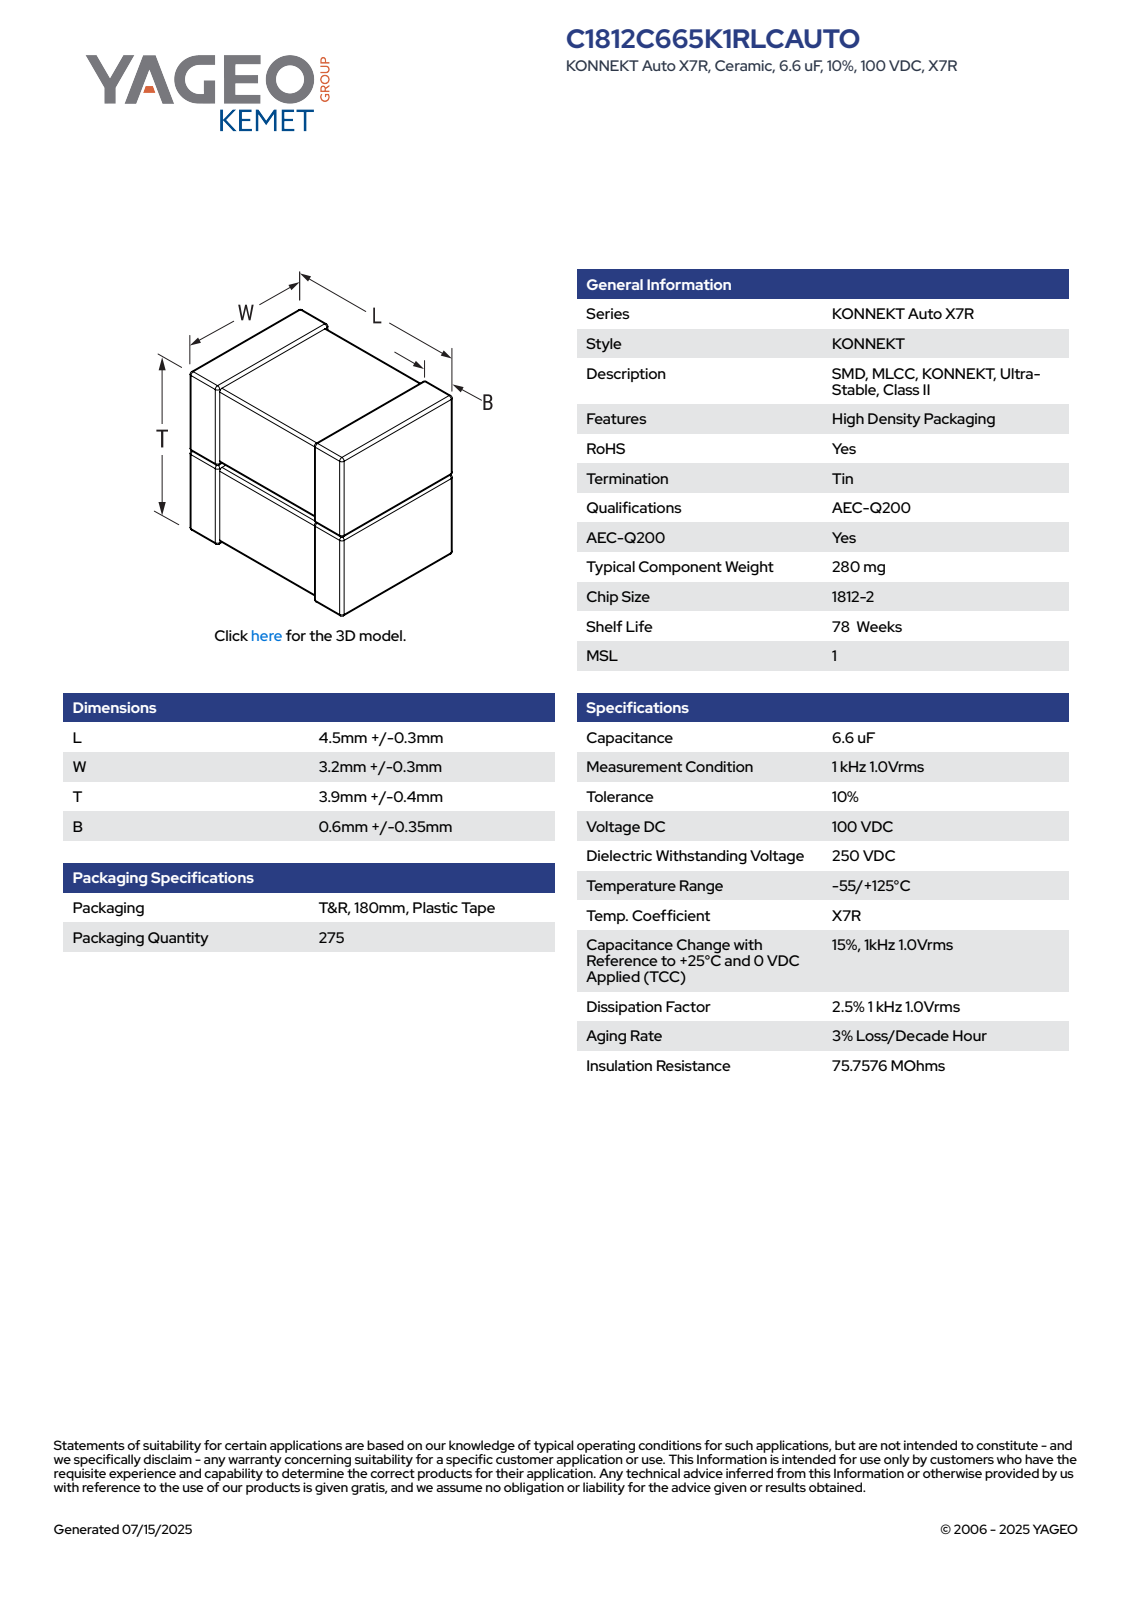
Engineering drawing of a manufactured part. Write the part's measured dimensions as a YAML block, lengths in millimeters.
part_name: "CCSS_K2T_1812-2_L4.8W3.5B0.95T4.3"
step_written_by: "SolidWorks 2020 (AUTOMOTIVE_DESIGN)"
units: millimeters
bodies: {solids: 4, faces: 197, planar: 81, cylindrical: 84, other: 32}
overall_size: [4.8, 4.3, 3.5]
volume: 68
surface_area: 125
face_to_face_distances: [2.01, 2.15, 4.8, 3.43, 2.08, 2.22, 4.23, 3.36, 4.16, 3.5]
